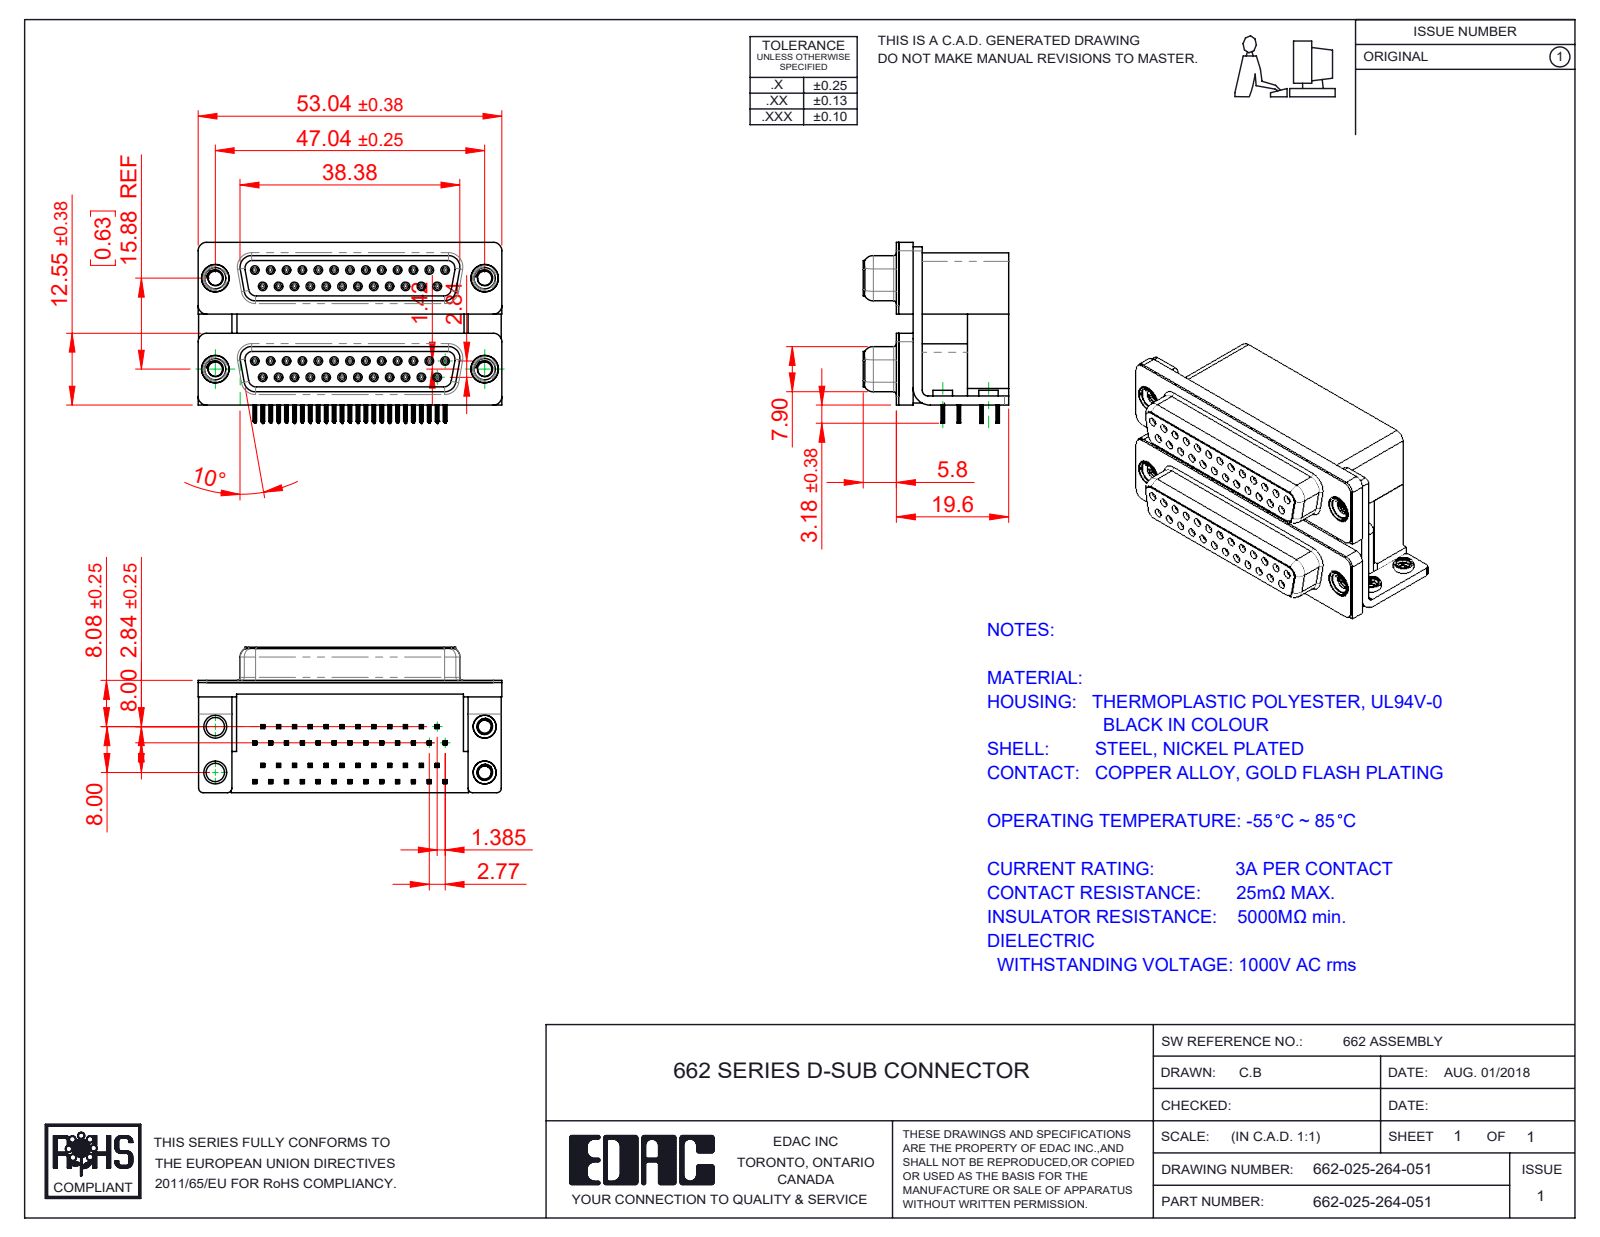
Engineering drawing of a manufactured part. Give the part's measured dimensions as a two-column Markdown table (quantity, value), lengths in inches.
| quantity | value |
| --- | --- |
| part name | 662 Contact Bottom Lower; 662 Contact Top Lower; 662 Housing Spacer_25 Contacts L; 662 Threaded Rivet_M3 (+8 more) |
| STEP written by | SolidWorks 2020 (CONFIG_CONTROL_DESIGN) |
| units | inches |
| bodies | 65 solids, 7936 faces (3588 planar, 1888 cylindrical, 2460 other) |
| overall size | 2.088 × 1.244 × 1 |
| volume | 1.399 in³ |
| surface area | 39.13 in² |
| round holes (diameter × count) | 0.031 × 50, 0.035 × 50, 0.089 × 4, 0.098 × 4, 0.108 × 4, 0.126 × 4, 0.138 × 4, 0.157 × 4, 0.189 × 4, 0.197 × 4 |
| round bosses / shafts (diameter × count) | 0.047 × 50, 0.193 × 4, 0.187 × 4, 0.157 × 4, 0.154 × 4, 0.134 × 4 |
| partial cylindrical surfaces (radius × count) | 0.004 × 400, 0.006 × 200, 0.014 × 100, 0.013 × 50, 0.011 × 24, 0.053 × 18, 0.059 × 13, 0.02 × 8 |
| main face-to-face distances | 0.625, 0.756, 0.016, 0.283, 0.472, 0.421, 0.244, 0.657, 0.374, 0.098 |
| hole center spacings | 0.124, 0.109, 0.218, 0.436, 0.327, 0.198, 0.545, 0.294 |
